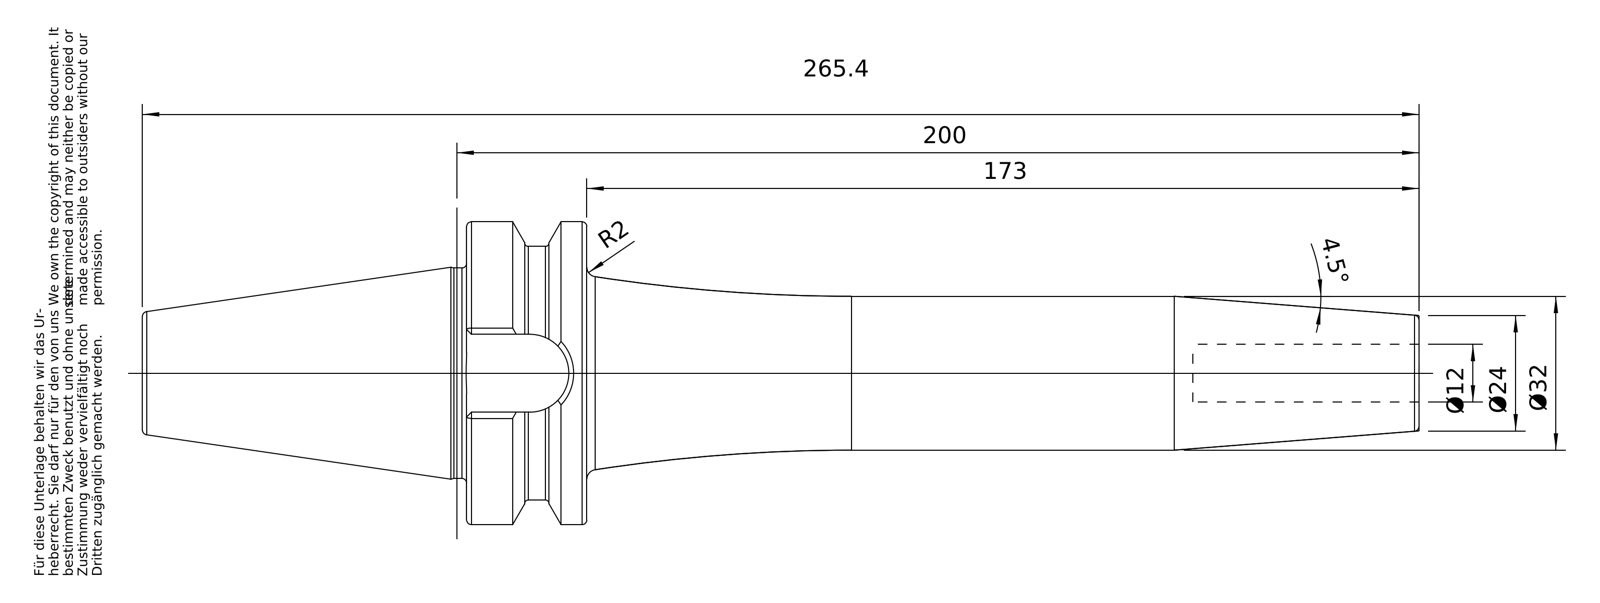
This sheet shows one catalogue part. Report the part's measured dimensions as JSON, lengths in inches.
{"part_name": "40-646-12", "step_written_by": "PRO/ENGINEER BY PARAMETRIC TECHNOLOGY CORPORATION, 2010430 (CONFIG_CONTROL_DESIGN)", "units": "inches", "bodies": {"solids": 1, "faces": 98, "planar": 26, "cylindrical": 22, "other": 50}, "overall_size": [10.449, 2.48, 2.48], "volume_in3": 15.82, "surface_area_in2": 61.92, "round_holes": [[0.472, 1], [0.545, 1], [0.67, 1], [0.689, 1]], "round_bosses_or_shafts": [[2.48, 1], [2.077, 1], [1.722, 1], [1.26, 1], [0.63, 1]], "partial_cylinders_radius": [[0.319, 1]], "face_to_face_distances": [0.984, 1.768, 7.795, 6.811, 0.638, 2.654, 3.638, 10.449, 8.598, 5.945]}
